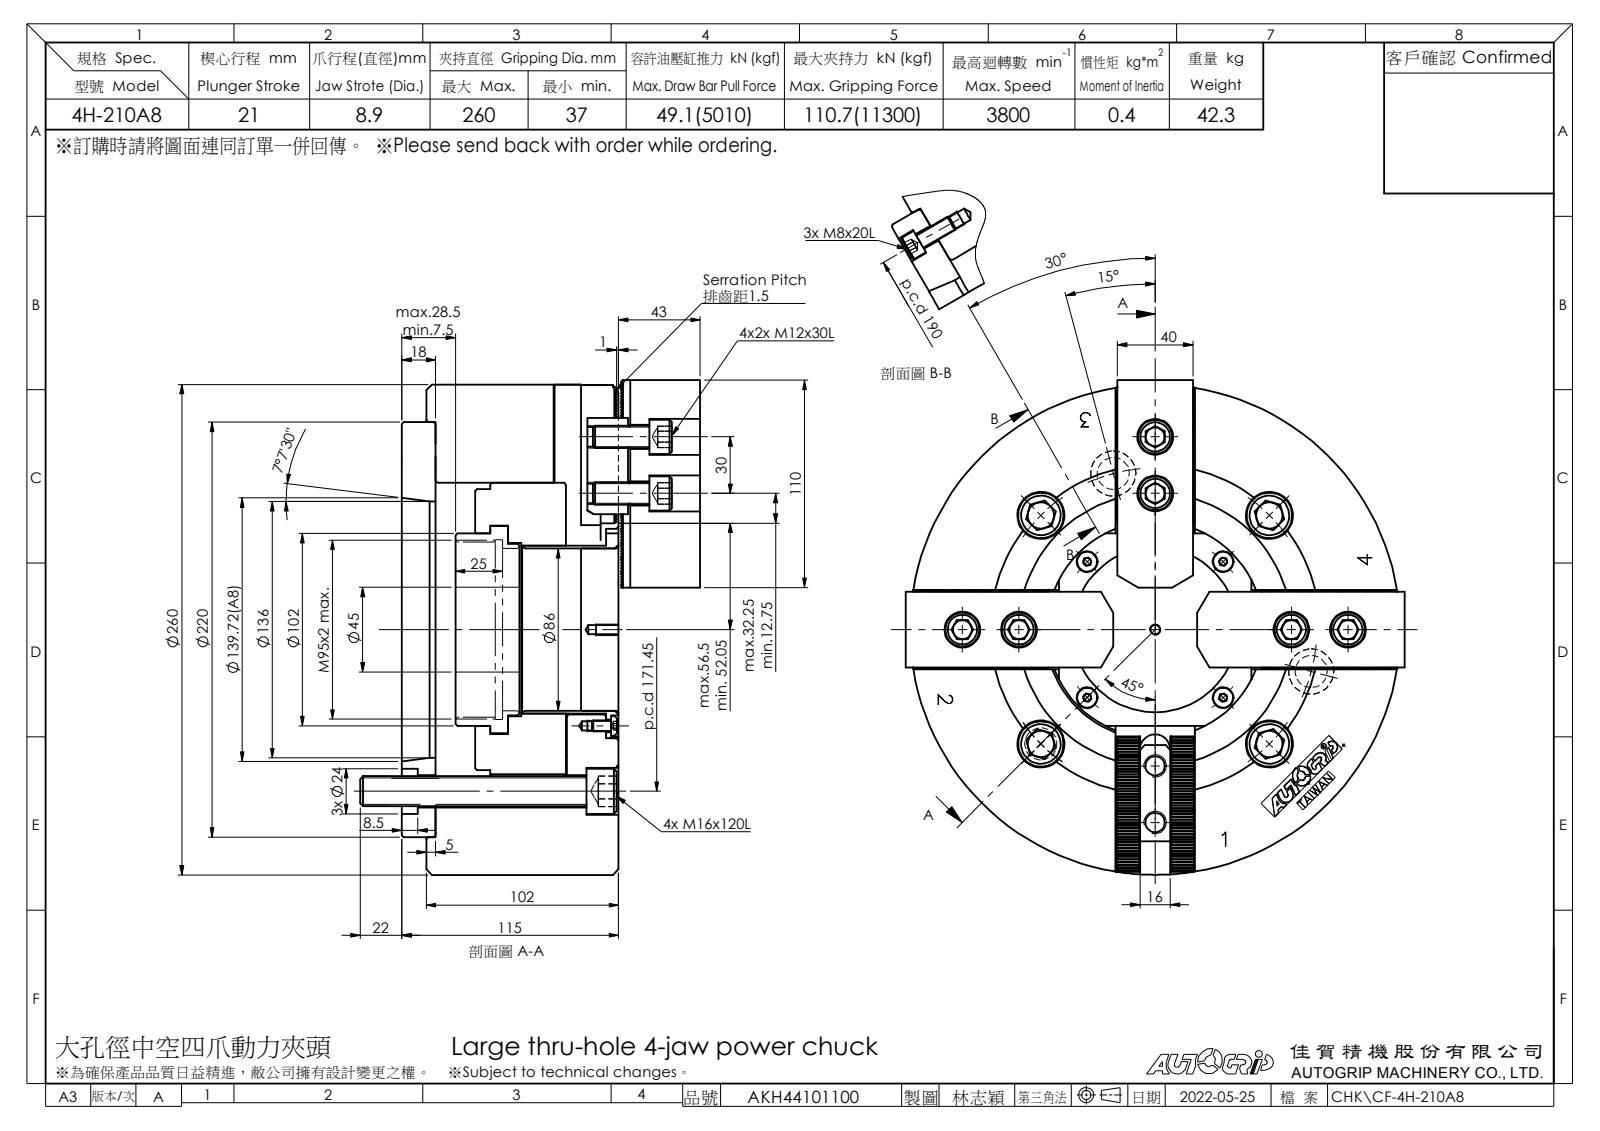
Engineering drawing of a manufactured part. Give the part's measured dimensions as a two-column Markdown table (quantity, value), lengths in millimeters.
| quantity | value |
| --- | --- |
| part name | CF-4H-210-01000; CF-3H-210-04000(T型塊); 圓頭內六角螺栓_M16x120; CF-4H-210-04000 (+8 more) |
| STEP written by | SolidWorks 2016 (CONFIG_CONTROL_DESIGN) |
| units | millimeters |
| bodies | 37 solids, 5129 faces (3642 planar, 1276 cylindrical, 211 other) |
| overall size | 264.5 × 264.5 × 180.3 |
| volume | 5 485 000 mm³ |
| surface area | 722 172 mm² |
| round holes (diameter × count) | 17 × 12, 10.2 × 8, 13 × 8, 19 × 8, 5 × 5, 6.8 × 5, 14 × 5, 6.6 × 4, 11 × 4, 25 × 4, 9 × 3, 24 × 3 |
| round bosses / shafts (diameter × count) | 18 × 8, 12 × 8, 16 × 4, 10.5 × 4, 6 × 4, 24 × 3, 13 × 3, 8 × 3 |
| partial cylindrical surfaces (radius × count) | 0.1 × 492, 8 × 4, 9 × 4, 135 × 4, 45 × 1, 57.5 × 1 |
| main face-to-face distances | 42, 97, 1, 41, 28, 13, 29, 12, 34, 40 |
| hole center spacings | 85.7, 44.36, 121.2, 148.44, 165.56, 69.68, 110.25, 143.47 |
